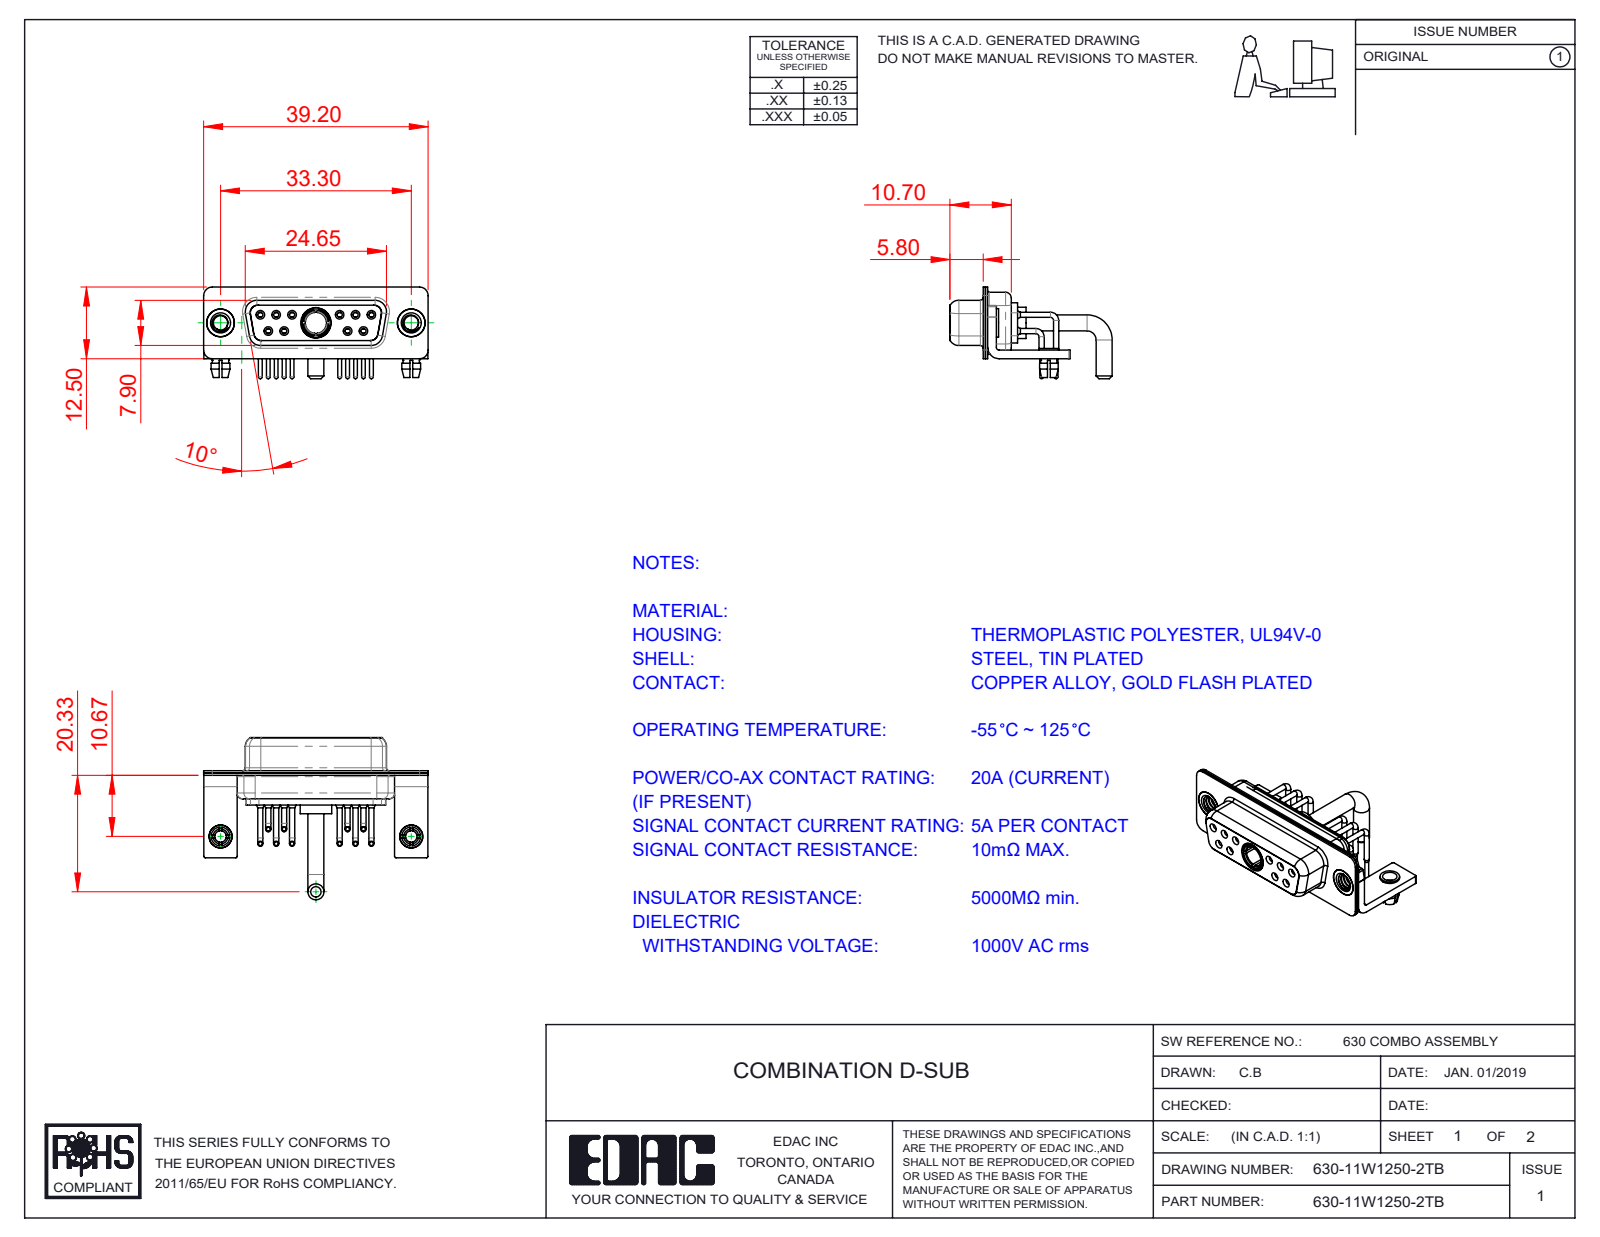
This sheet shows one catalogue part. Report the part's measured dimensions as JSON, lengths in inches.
{"part_name": "630Combo Shell Rear_15 Contacts; 630-11W1250-2TB; 630Combo Contact Row 1; 630Combo Stabilizer Bracket (+6 more)", "step_written_by": "SolidWorks 2020 (CONFIG_CONTROL_DESIGN)", "units": "inches", "bodies": {"solids": 21, "faces": 1017, "planar": 314, "cylindrical": 442, "other": 261}, "overall_size": [1.543, 1.115, 0.63], "volume_in3": 0.182, "surface_area_in2": 11.06, "round_holes": [[0.079, 12], [0.035, 10], [0.043, 10], [0.059, 10], [0.067, 6], [0.063, 4], [0.098, 4], [0.191, 3], [0.126, 2], [0.157, 2], [0.159, 2], [0.146, 1]], "round_bosses_or_shafts": [[0.035, 10], [0.026, 10], [0.063, 6], [0.197, 2], [0.195, 2], [0.189, 2], [0.157, 2], [0.134, 2]], "partial_cylinders_radius": [[0.01, 16], [0.059, 16], [0.079, 13], [0.053, 12], [0.063, 8], [0.02, 5], [0.024, 4], [0.026, 4]], "face_to_face_distances": [0.016, 0.031, 0.018, 0.055, 0.333, 0.059, 0.071, 0.35, 0.244, 0.091], "hole_center_spacings": [0.124, 0.109, 0.545, 0.436, 0.654, 0.198, 0.198, 0.218]}
